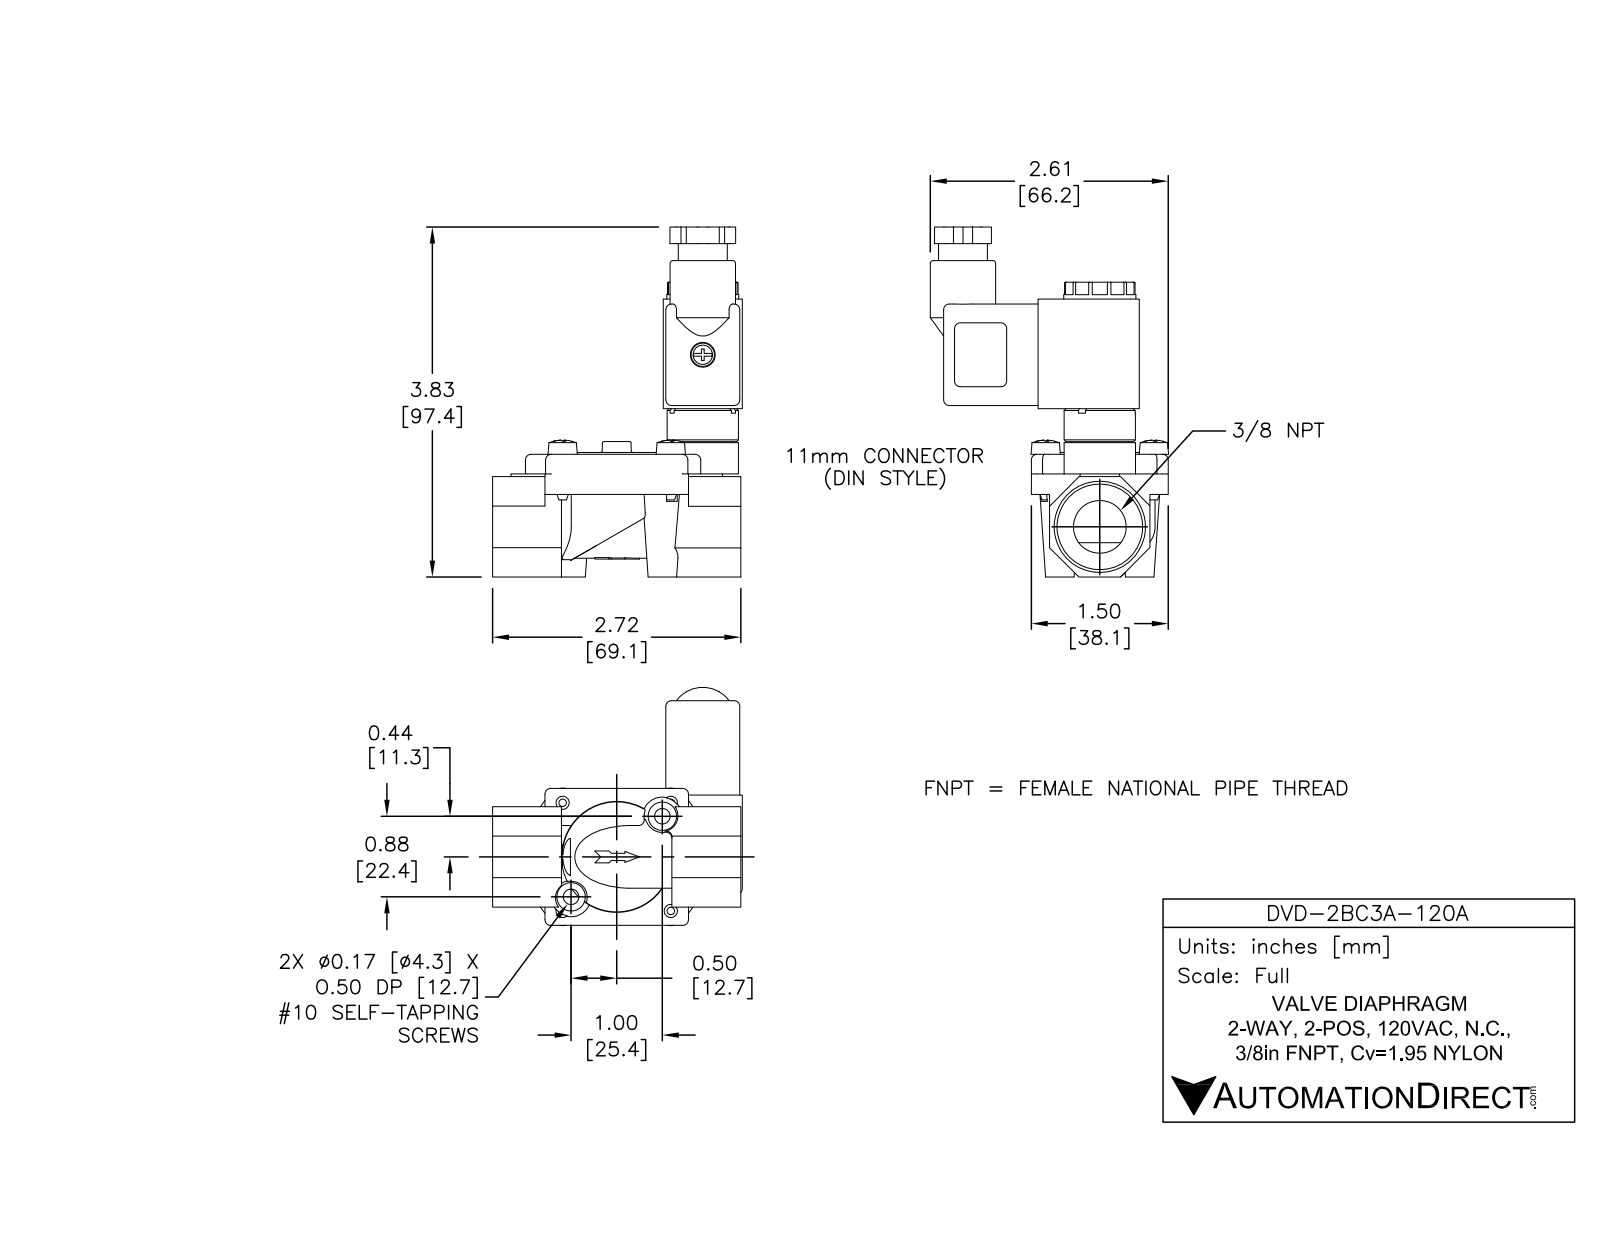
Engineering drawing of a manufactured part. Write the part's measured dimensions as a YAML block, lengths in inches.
part_name: "DVD-2BC3A-120A"
step_written_by: "SolidWorks 2015 (AUTOMOTIVE_DESIGN)"
units: inches
bodies: {solids: 13, faces: 1441, planar: 721, cylindrical: 253, other: 467}
overall_size: [3.834, 2.736, 2.611]
volume: 4.016
surface_area: 62.17
round_holes:
  - {diameter: 0.144, count: 4}
  - {diameter: 0.164, count: 4}
  - {diameter: 0.06, count: 2}
  - {diameter: 0.093, count: 2}
  - {diameter: 0.17, count: 2}
  - {diameter: 0.578, count: 2}
  - {diameter: 0.062, count: 1}
  - {diameter: 0.156, count: 1}
  - {diameter: 0.166, count: 1}
  - {diameter: 0.25, count: 1}
  - {diameter: 0.272, count: 1}
  - {diameter: 0.312, count: 1}
round_bosses_or_shafts:
  - {diameter: 0.187, count: 4}
  - {diameter: 0.125, count: 4}
  - {diameter: 0.625, count: 2}
  - {diameter: 1.375, count: 1}
  - {diameter: 0.79, count: 1}
  - {diameter: 0.782, count: 1}
  - {diameter: 0.781, count: 1}
  - {diameter: 0.716, count: 1}
partial_cylinders:
  - {radius: 0.01, count: 24}
  - {radius: 0.062, count: 24}
  - {radius: 0.156, count: 12}
  - {radius: 0.044, count: 3}
  - {radius: 0.094, count: 2}
  - {radius: 0.215, count: 2}
  - {radius: 0.304, count: 1}
  - {radius: 0.344, count: 1}
face_to_face_distances: [0.05, 1.1, 0.866, 0.76, 0.2, 1.3, 0.788, 0.078, 0.078, 0.71]
hole_center_spacings: [0.838, 1.185, 0.181, 0.664, 0.688, 1.034, 1.104, 1.502]
